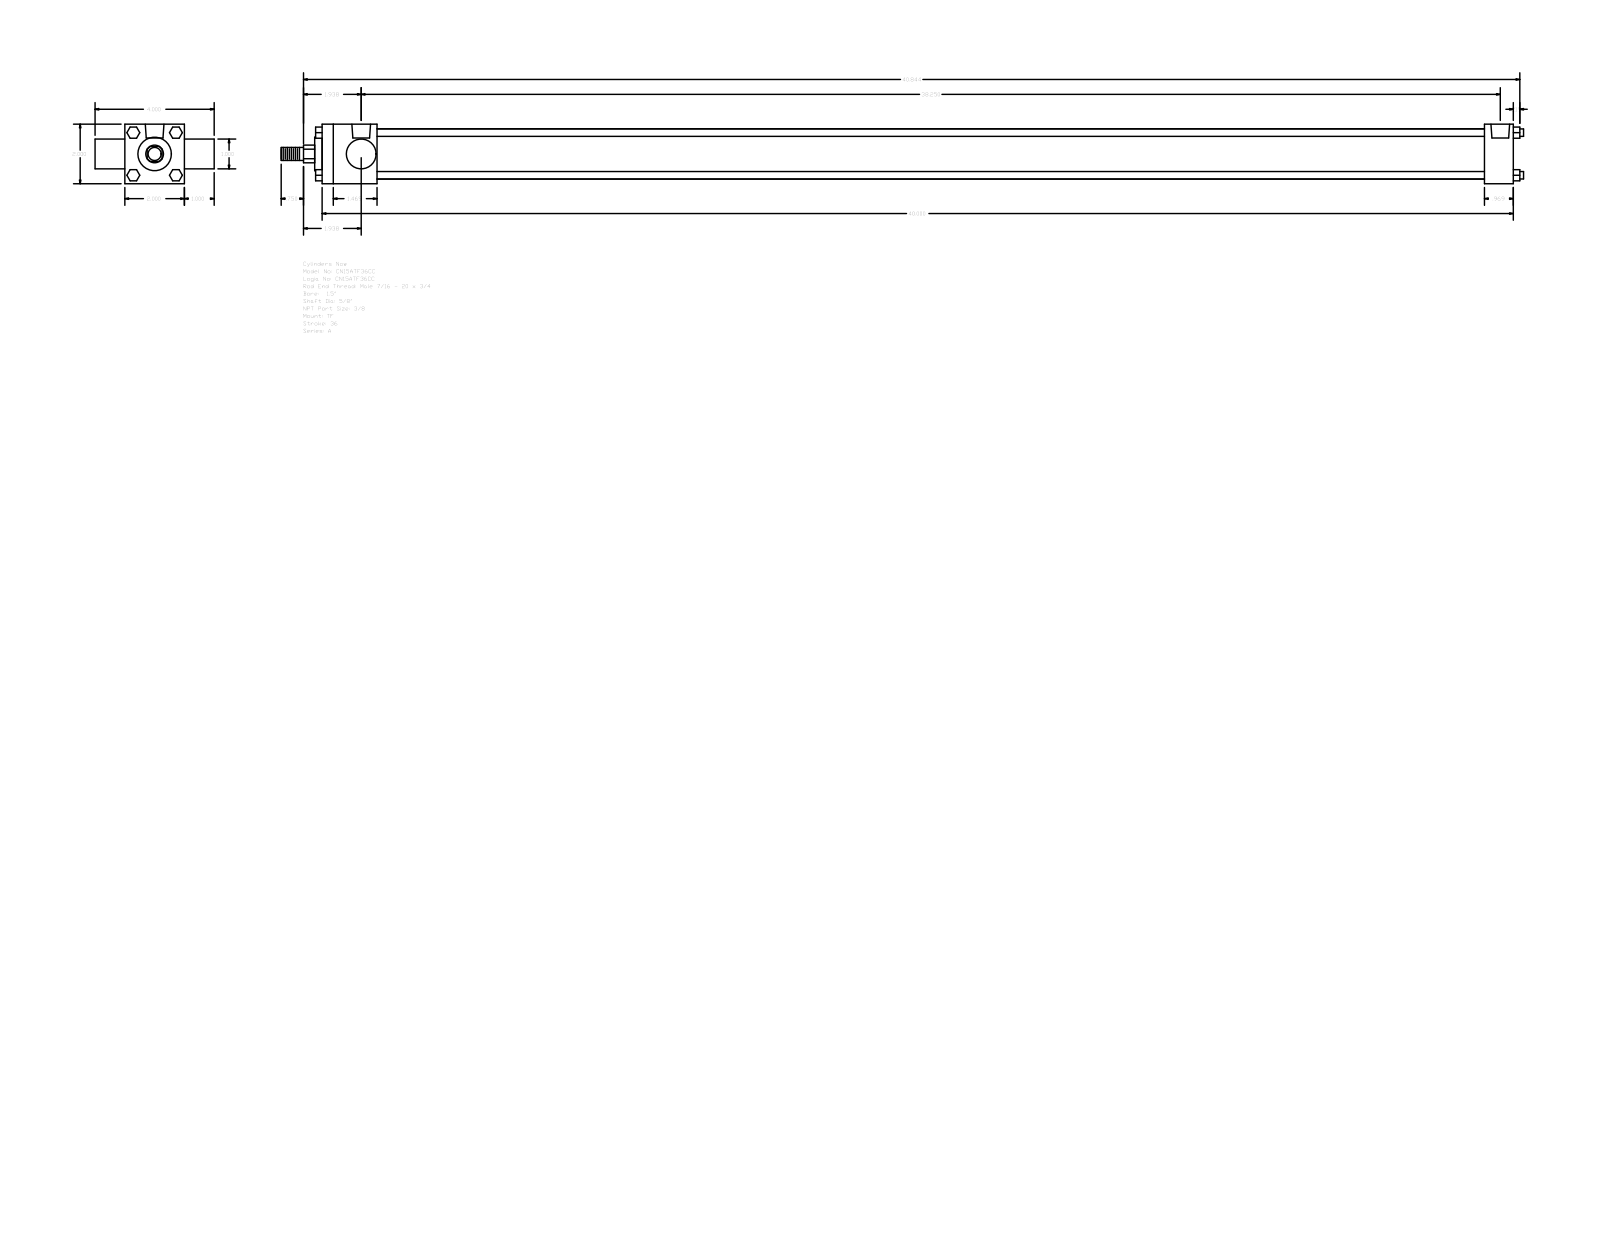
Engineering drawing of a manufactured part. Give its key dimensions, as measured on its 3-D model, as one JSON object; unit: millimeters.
{"part_name": "A_TF__0150_0.625", "step_written_by": "GSSL Pune (CONFIG_CONTROL_DESIGN)", "units": "millimeters", "bodies": {"solids": 0, "faces": 120, "planar": 92, "cylindrical": 28, "other": 0}, "overall_size": [1059.66, 101.6, 50.8], "round_holes": [[5.56, 3], [15.93, 2]], "round_bosses_or_shafts": [[6.35, 4], [42.93, 1], [28.57, 1], [25.4, 1], [15.88, 1], [11.11, 1]], "partial_cylinders_radius": [[7.54, 1]], "face_to_face_distances": [50.8, 1016, 25.4, 76.2, 46.83, 991.39, 944.56, 969.17, 24.61, 101.6], "hole_center_spacings": [3.97, 967.58, 963.61, 971.55]}
